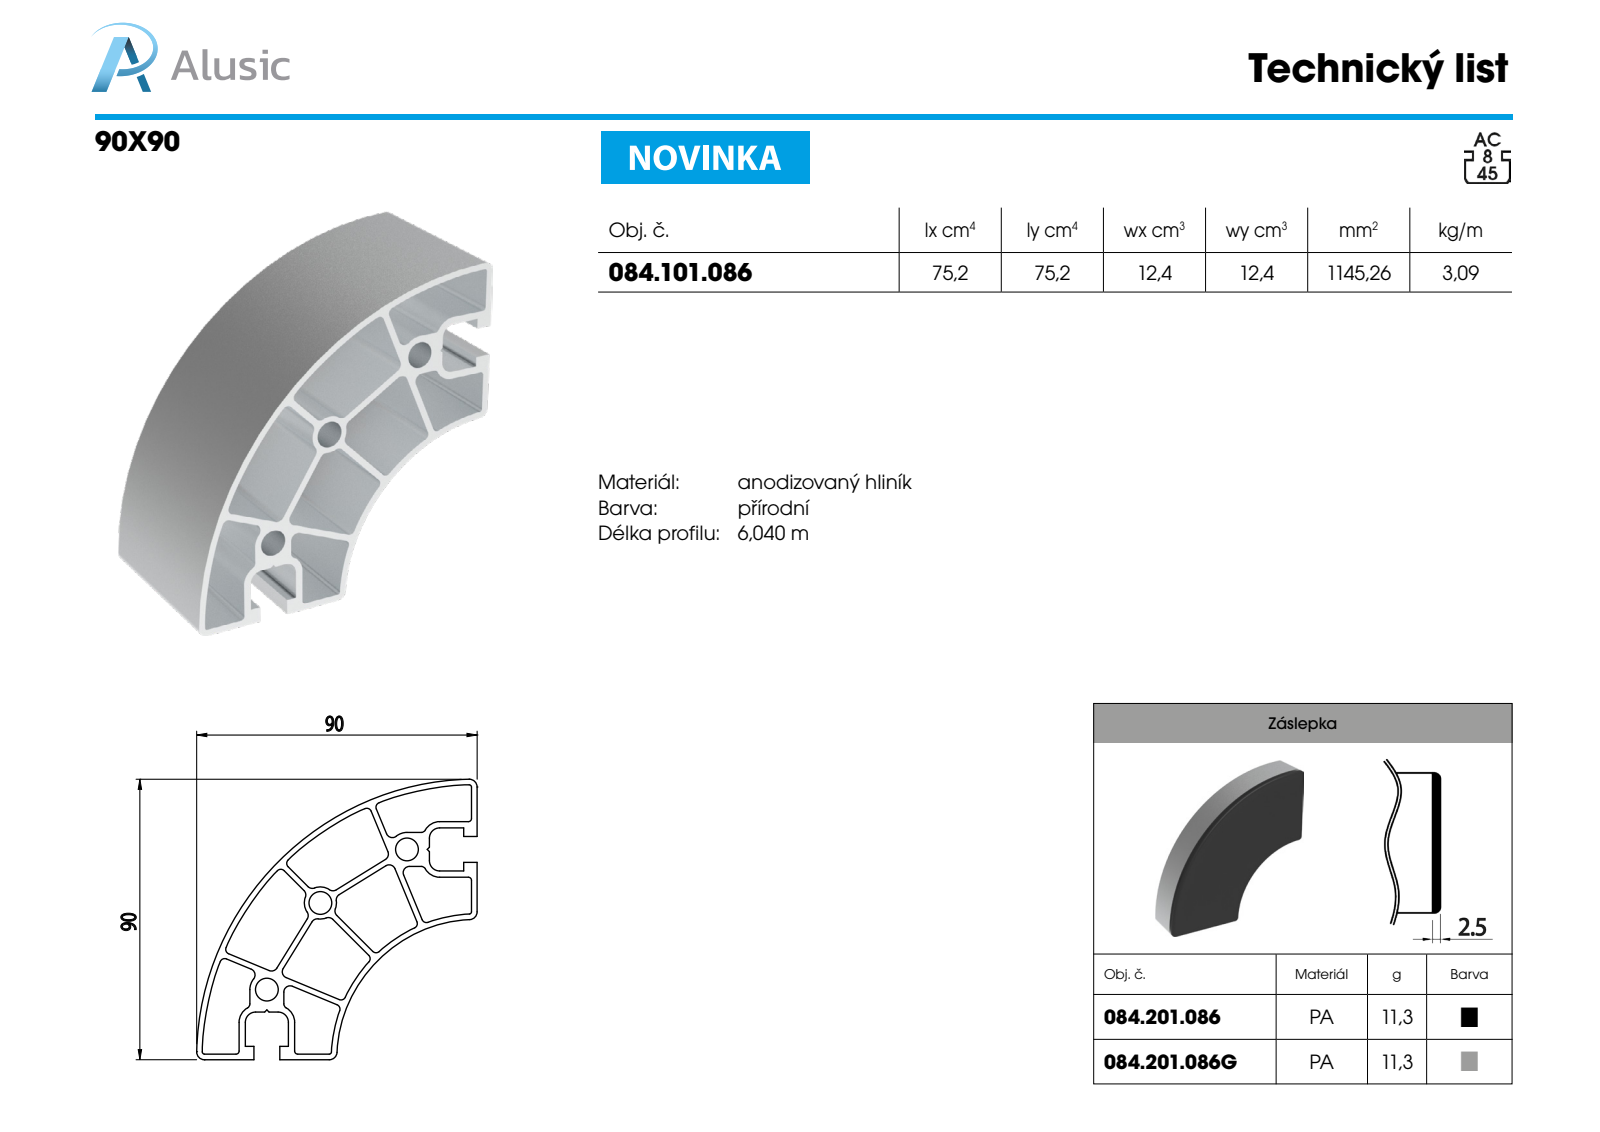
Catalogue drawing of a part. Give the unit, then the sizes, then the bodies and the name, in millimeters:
Units: millimetres
Overall size (bounding box): 100 × 89.96 × 89.96
Round holes (diameter × count): ⌀7.3 ×3
Partial cylindrical surfaces — rounded edges, fillets, slot ends (radius × count): R1.5 ×16, R2 ×16, R0.7 ×4, R1 ×4, R2.5 ×4, R3.3 ×4, R5.3 ×4, R5.45 ×2
Main face-to-face distances: 1.8, 2, 15.82, 1.79, 1.81, 74.56, 76.36, 17.82, 56.74, 58.54
Hole centre spacings: 32.66, 63.57
Volume: 114 526 mm³ · Surface area: 110 846 mm²
Bodies: 1 solid, 138 faces (54 planar, 84 cylindrical, 0 other)
Part name (STEP PRODUCT): 084.101.086
STEP written by: SolidWorks 2018 (AUTOMOTIVE_DESIGN)
